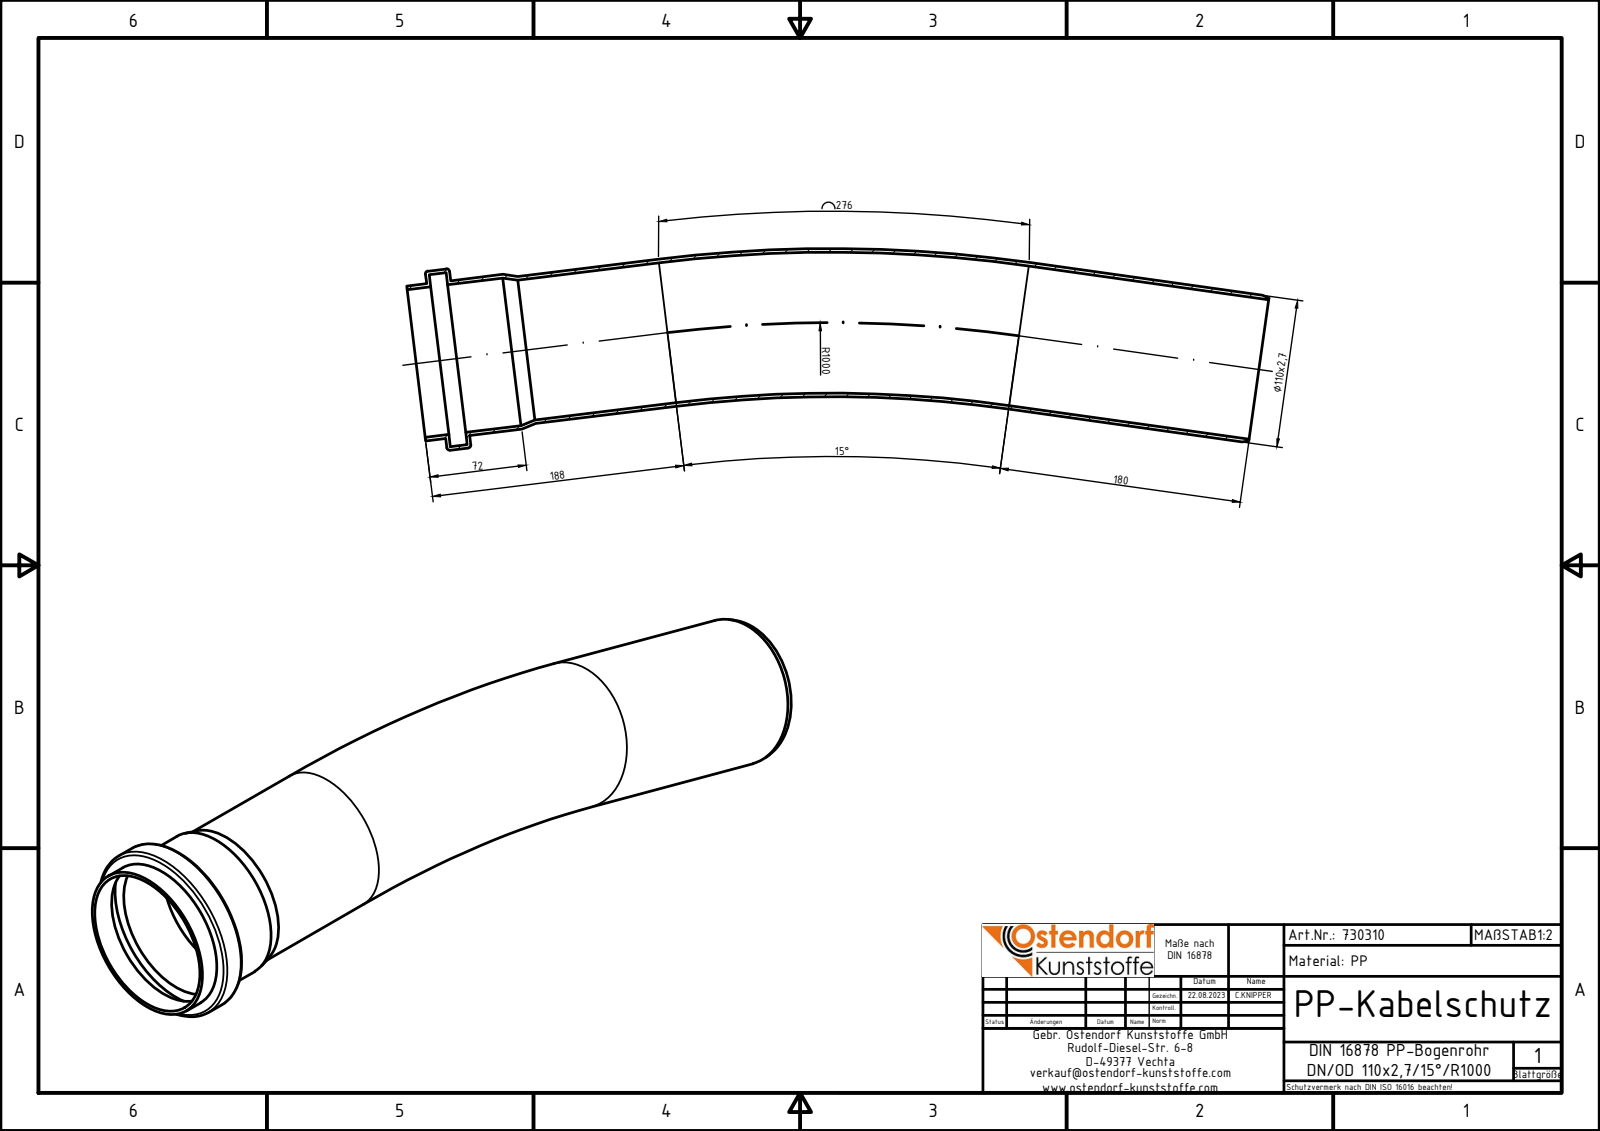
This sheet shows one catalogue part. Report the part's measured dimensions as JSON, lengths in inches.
{"part_name": "PP-Bogenrohr_110x27_R1000_15_SM_34873_730310", "step_written_by": "Autodesk Inventor 2024 (AUTOMOTIVE_DESIGN)", "units": "inches", "bodies": {"solids": 1, "faces": 23, "planar": 6, "cylindrical": 10, "other": 7}, "overall_size": [24.983, 7.854, 5.276], "volume_in3": 36.41, "surface_area_in2": 688.4, "round_holes": [[4.118, 2], [4.346, 1], [5.063, 1]], "round_bosses_or_shafts": [[4.331, 2], [5.276, 1], [4.559, 1]], "face_to_face_distances": [0.496, 0.603, 0.107, 0.106, 0.602, 0.709, 0.591, 0.696, 1.193, 1.299]}
